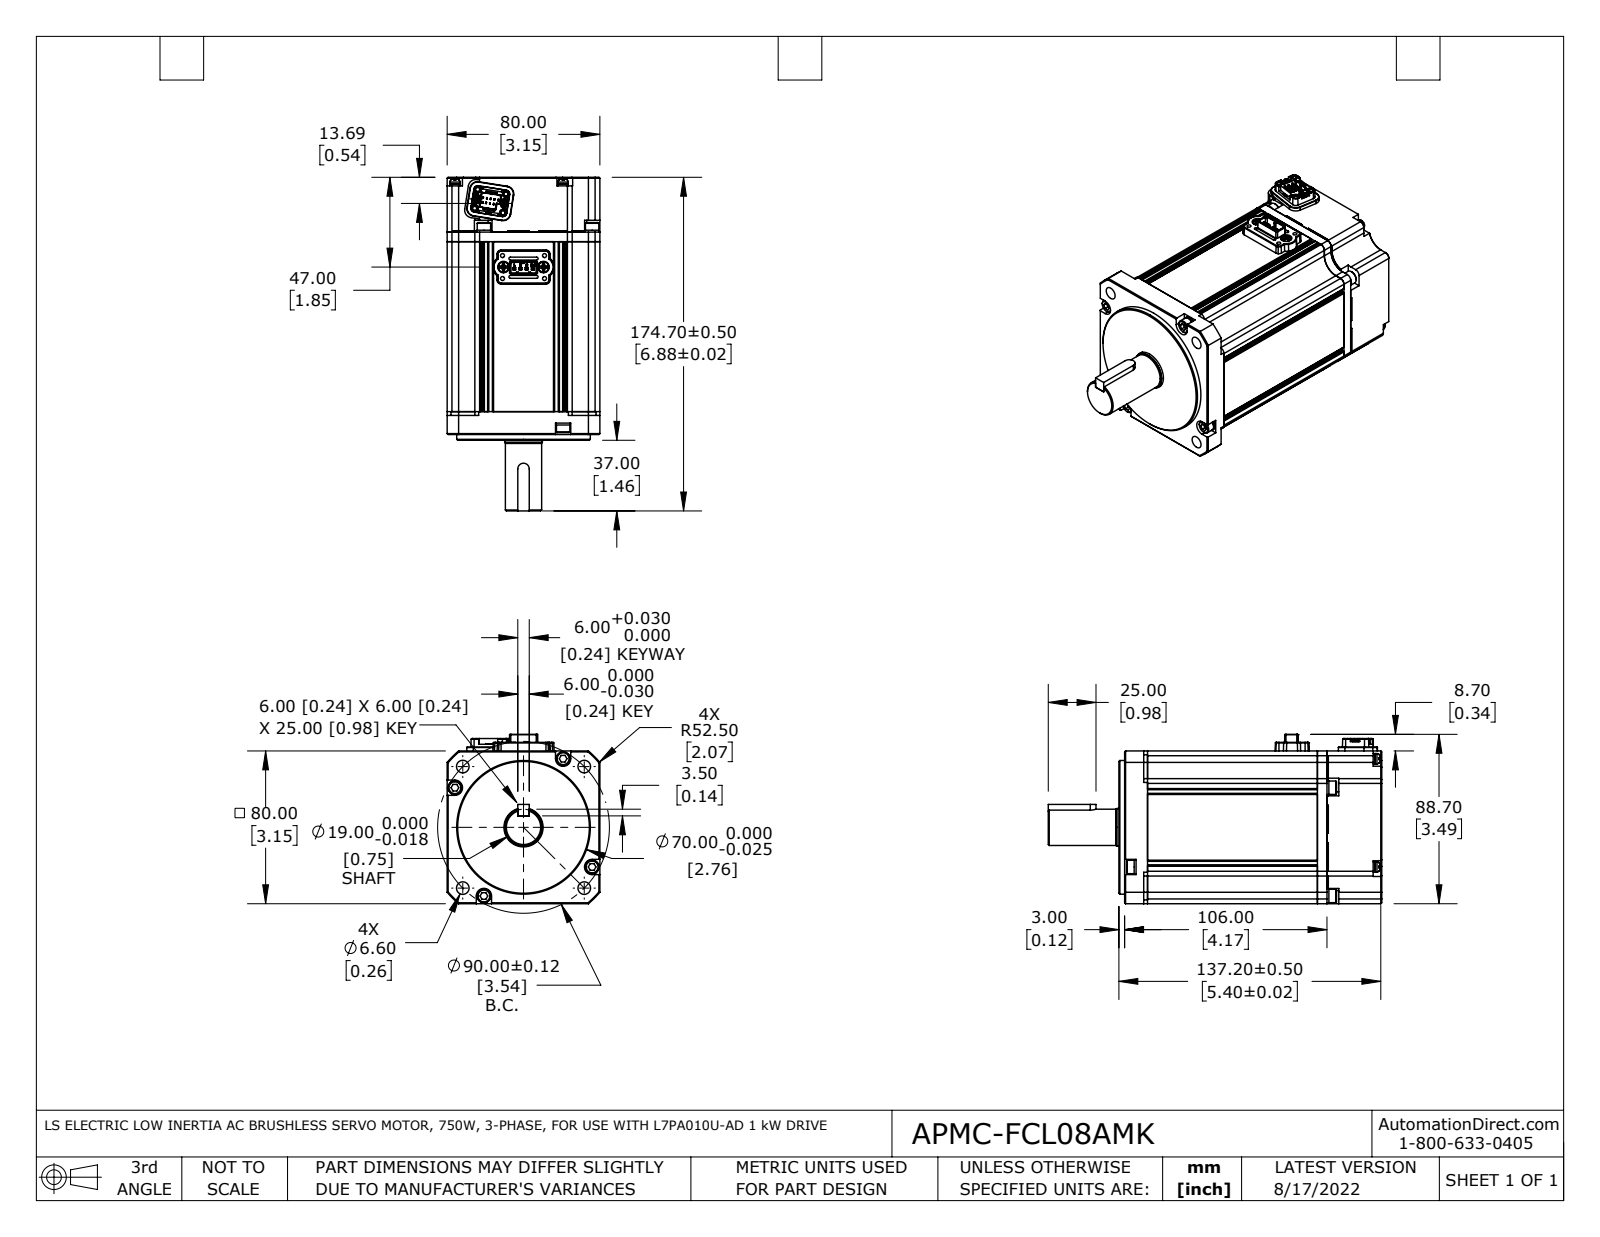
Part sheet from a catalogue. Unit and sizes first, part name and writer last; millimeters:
Units: millimetres
Overall size (bounding box): 174.7 × 88.7 × 80
Round holes (diameter × count): ⌀2.1 ×10, ⌀4 ×8, ⌀4.5 ×8, ⌀3 ×6, ⌀3.5 ×4, ⌀6.6 ×4, ⌀2 ×2, ⌀6 ×2, ⌀3.3 ×1, ⌀3.4 ×1, ⌀20.5 ×1
Round bosses / shafts (diameter × count): ⌀7.2 ×8, ⌀7 ×8, ⌀5.4 ×6, ⌀2.2 ×2, ⌀70 ×1, ⌀19.8 ×1, ⌀19 ×1
Partial cylindrical surfaces — rounded edges, fillets, slot ends (radius × count): R0.3 ×36, R0.2 ×20, R0.2 ×9, R2.5 ×9, R1 ×8, R2 ×8, R0.5 ×7, R0.1 ×6
Main face-to-face distances: 5, 80, 89, 94, 0.7, 5.7, 94.7, 28, 28.7, 33.7
Hole centre spacings: 41.5, 11.8, 52.7, 58.7, 68.7, 85.8, 6, 16
Volume: 781 700 mm³ · Surface area: 118 500 mm²
Bodies: 45 solids, 1860 faces (1195 planar, 483 cylindrical, 182 other)
Part name (STEP PRODUCT): SLM08GA001G03_Out Line(APMC-FCL08AMK) r1 nc fxt
STEP written by: SolidWorks 2017 (AUTOMOTIVE_DESIGN)
